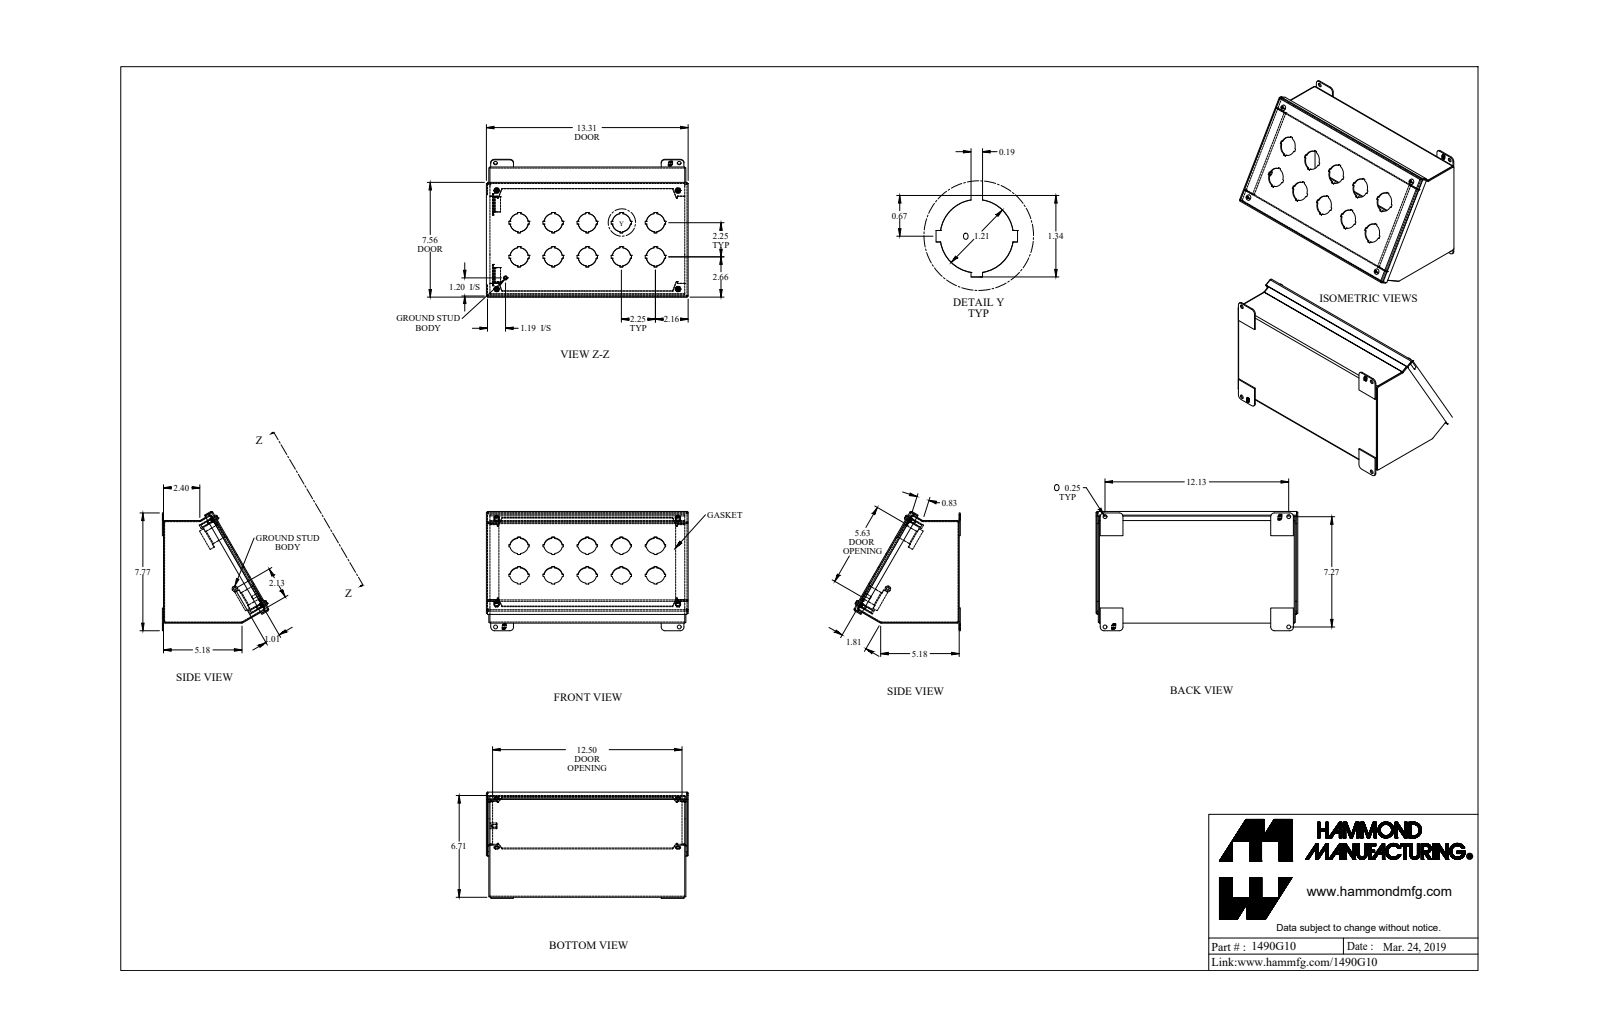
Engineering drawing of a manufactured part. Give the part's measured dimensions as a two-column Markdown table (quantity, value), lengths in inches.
| quantity | value |
| --- | --- |
| part name | 1490G10_Default |
| STEP written by | SolidWorks 2019 (CONFIG_CONTROL_DESIGN) |
| units | inches |
| bodies | 28 solids, 869 faces (625 planar, 204 cylindrical, 40 other) |
| overall size | 13.312 × 7.869 × 7.008 |
| volume | 35.25 in³ |
| surface area | 924.7 in² |
| round holes (diameter × count) | 1.21 × 10, 0.25 × 8, 0.159 × 4, 0.156 × 1 |
| round bosses / shafts (diameter × count) | 0.39 × 4, 0.275 × 4, 0.19 × 4, 0.148 × 4, 0.375 × 1, 0.25 × 1, 0.188 × 1 |
| partial cylindrical surfaces (radius × count) | 0.108 × 18, 0.036 × 12, 0.25 × 8, 0.029 × 7, 0.086 × 7, 0.125 × 4, 0.16 × 4, 0.171 × 4 |
| main face-to-face distances | 0.072, 12.928, 6.698, 12.856, 13, 6.77, 6.626, 0.259, 0.187, 0.153 |
| hole center spacings | 2.25, 3.182, 4.5, 5.031, 2.25, 2.589, 4.293, 4.619 |
